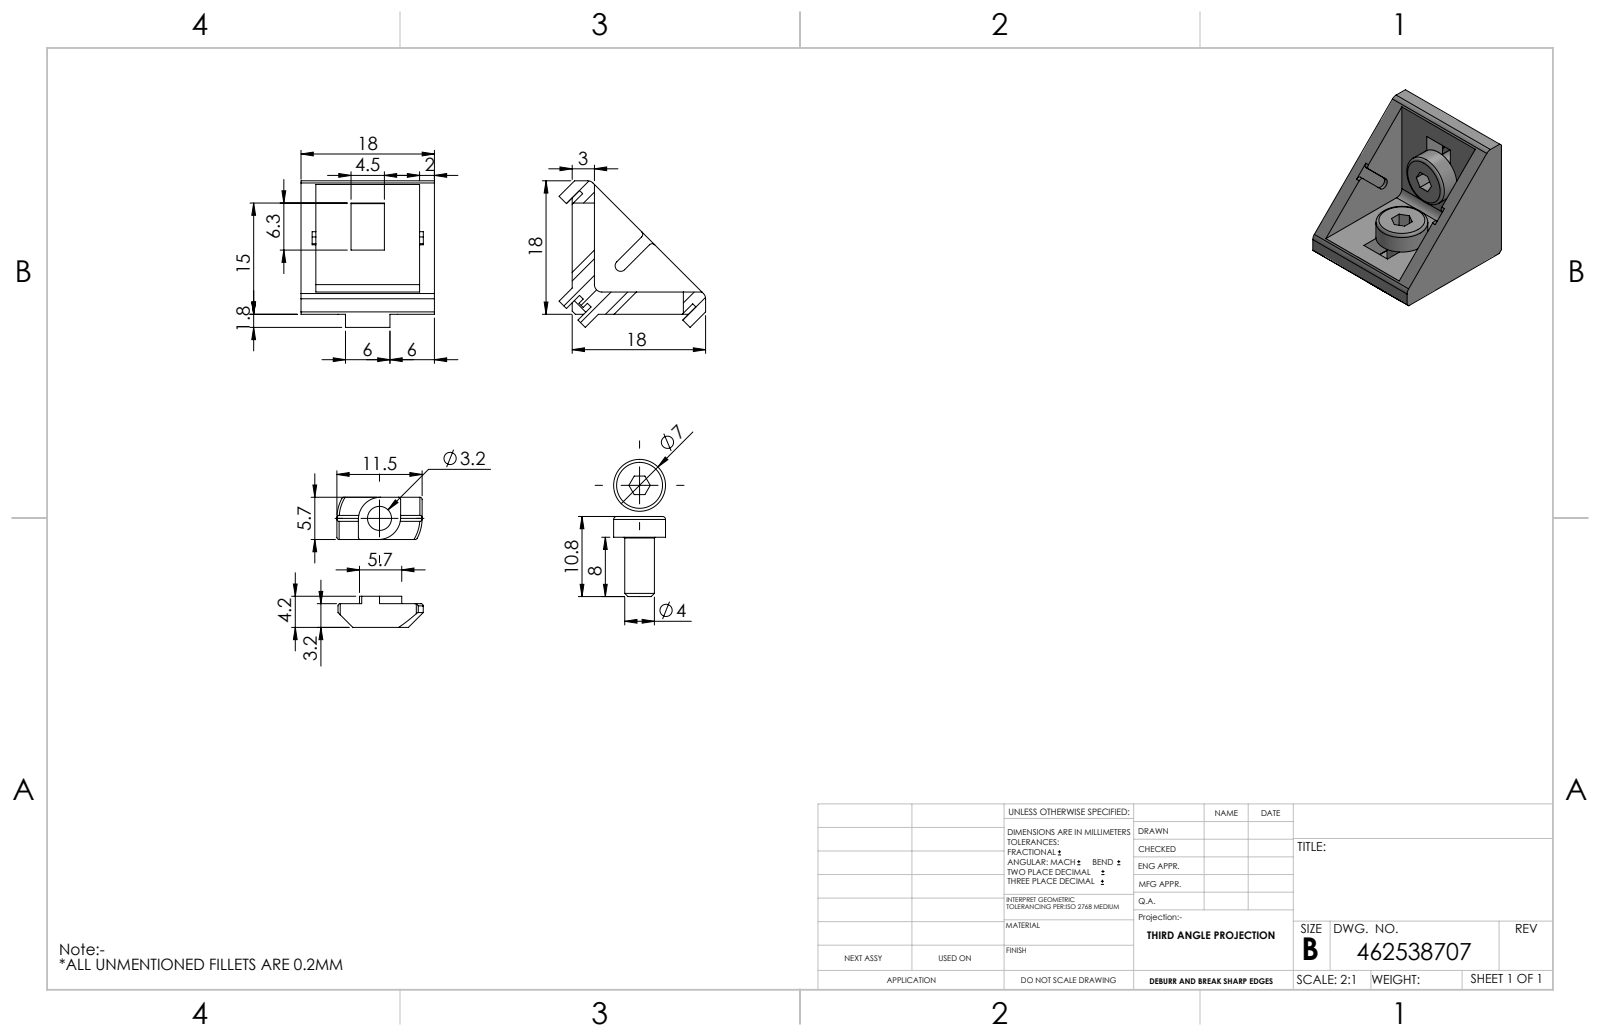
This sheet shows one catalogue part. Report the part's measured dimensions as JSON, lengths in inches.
{"part_name": "Syskomp 462538707 Winkel 20x20 inkl Bef; Syskomp 462523508 Winkel 20x20; Syskomp 462523135 Hammermutter N6 M4 verzinkt; DIN 7984 M4 x 8", "step_written_by": "Autodesk Inventor 2012 (AUTOMOTIVE_DESIGN)", "units": "inches", "bodies": {"solids": 5, "faces": 195, "planar": 140, "cylindrical": 39, "other": 16}, "overall_size": [0.906, 0.906, 0.709], "volume_in3": 0.155, "surface_area_in2": 4.951, "round_holes": [[0.128, 2]], "round_bosses_or_shafts": [[0.276, 2], [0.157, 2]], "partial_cylinders_radius": [[0.012, 16], [0.118, 4], [0.039, 3], [0.02, 2], [0.226, 2], [0.03, 1]], "face_to_face_distances": [0.118, 0.059, 0.079, 0.709, 0.63, 0.177, 0.394, 0.65, 0.591, 0.138]}
